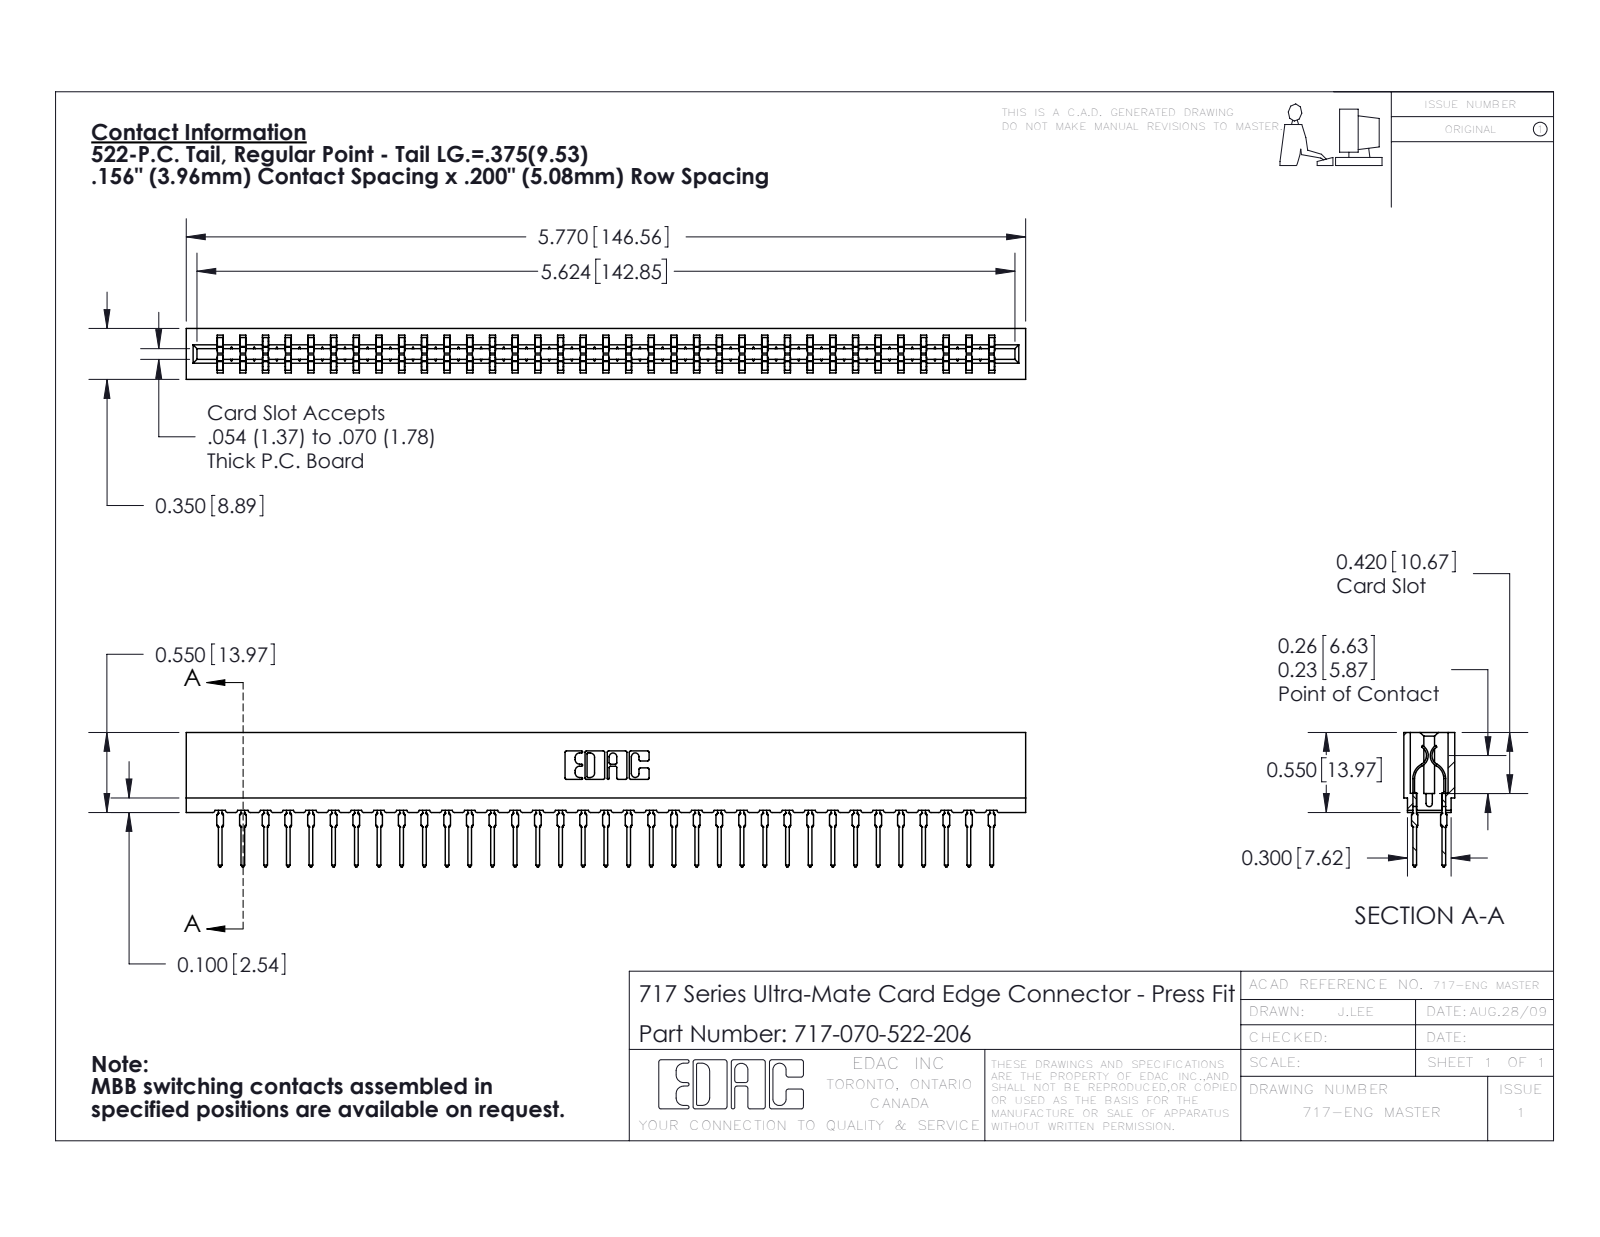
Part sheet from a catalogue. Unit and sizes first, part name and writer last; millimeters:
Units: millimetres
Overall size (bounding box): 146.6 × 23.5 × 8.9
Partial cylindrical surfaces — rounded edges, fillets, slot ends (radius × count): R0.5 ×140, R0.4 ×70, R0.3 ×22, R0.1 ×8, R0.3 ×8, R0.2 ×6, R0.8 ×6, R0.7 ×3
Main face-to-face distances: 5.4, 3.5, 8.9, 1.6, 7.3, 1.9, 3.8, 1.9, 1.1, 7.7
Volume: 12 800 mm³ · Surface area: 19 770 mm²
Bodies: 71 solids, 6394 faces (3309 planar, 1265 cylindrical, 1820 other)
Part name (STEP PRODUCT): 717-070-522-206; 745-292-001_522; 717 Part_Insulator Option - 06
STEP written by: SolidWorks 2016 (CONFIG_CONTROL_DESIGN)
